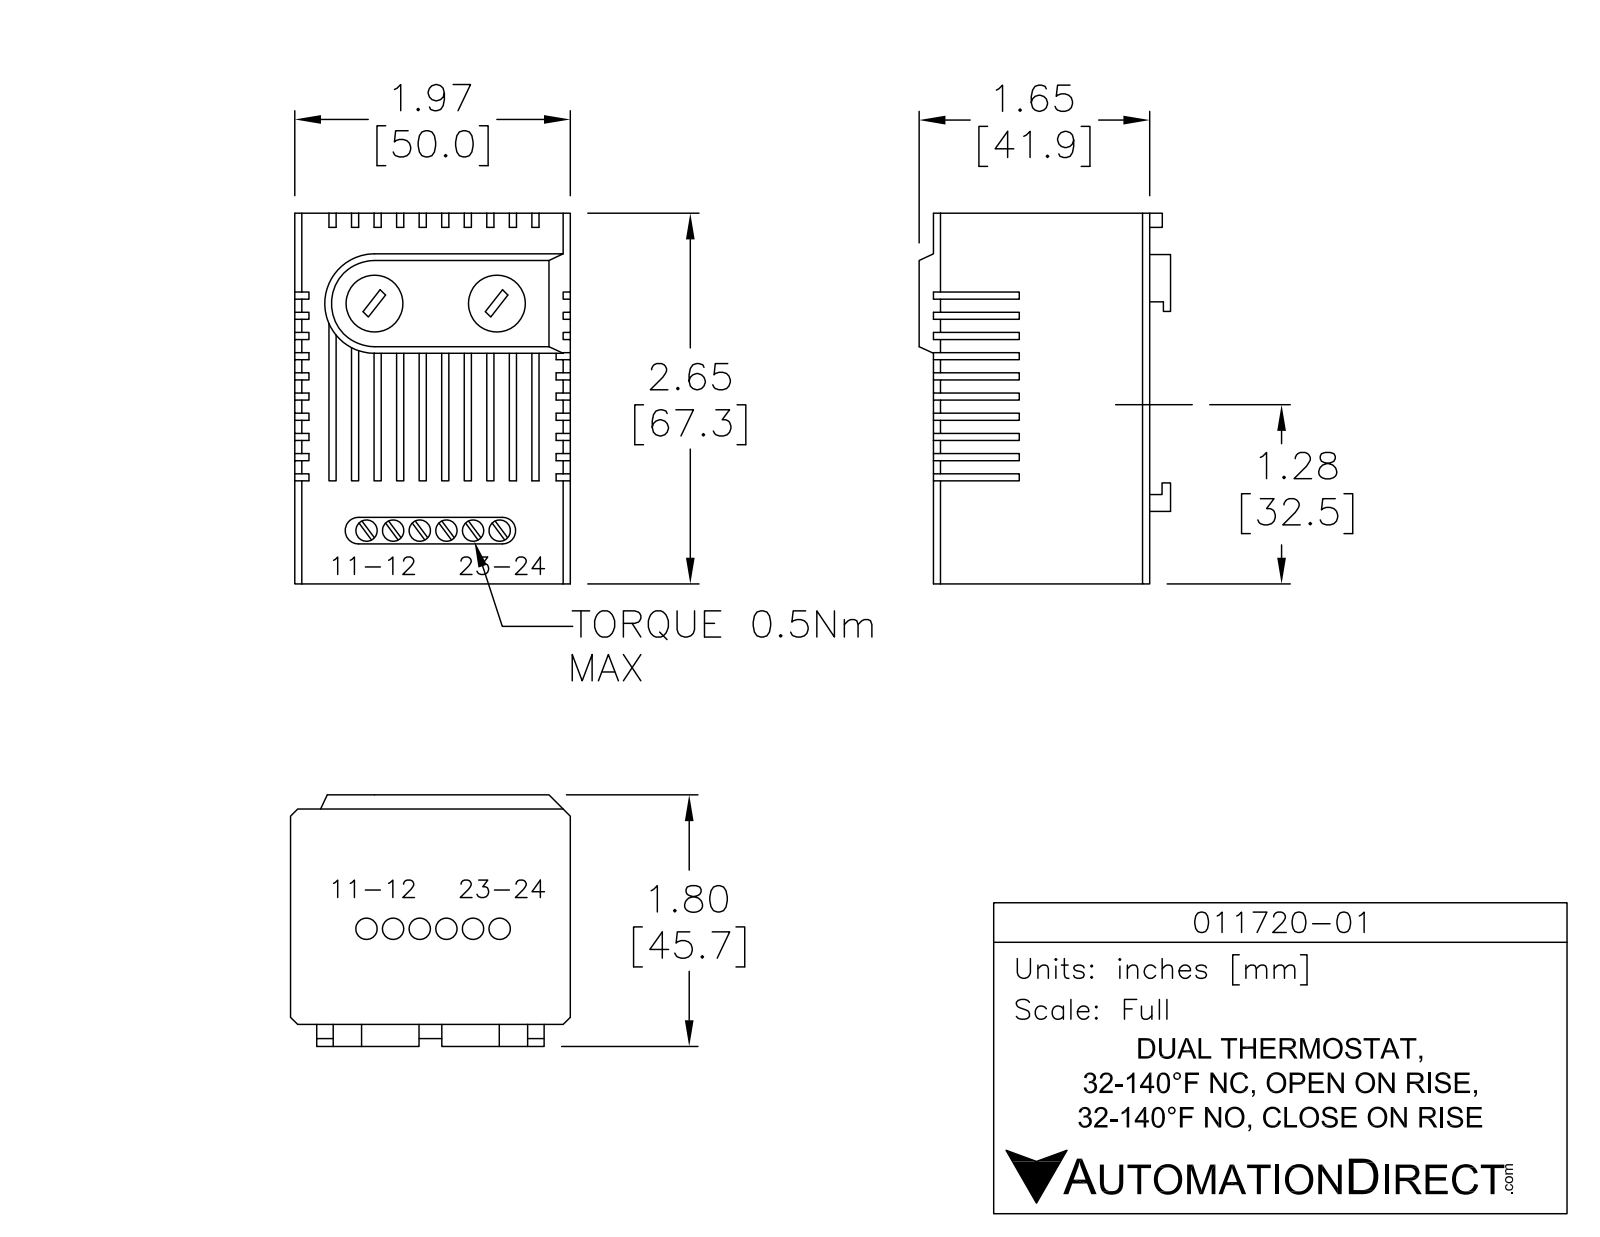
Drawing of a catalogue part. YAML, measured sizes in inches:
part_name: "011720-01"
step_written_by: "SolidWorks 2013 (AUTOMOTIVE_DESIGN)"
units: inches
bodies: {solids: 1, faces: 442, planar: 353, cylindrical: 80, other: 9}
overall_size: [2.645, 1.97, 1.8]
volume: 6.887
surface_area: 56.19
round_holes:
  - {diameter: 0.15, count: 6}
  - {diameter: 0.16, count: 6}
  - {diameter: 0.385, count: 1}
  - {diameter: 0.385, count: 1}
partial_cylinders:
  - {radius: 0.06, count: 8}
  - {radius: 0.065, count: 2}
  - {radius: 0.145, count: 2}
face_to_face_distances: [0.122, 0.244, 0.366, 0.06, 0.732, 0.488, 0.61, 0.854, 0.976, 0.304]
hole_center_spacings: [0.195, 0.585, 0.39, 0.39, 0.78, 0.195, 0.975, 0.79]
